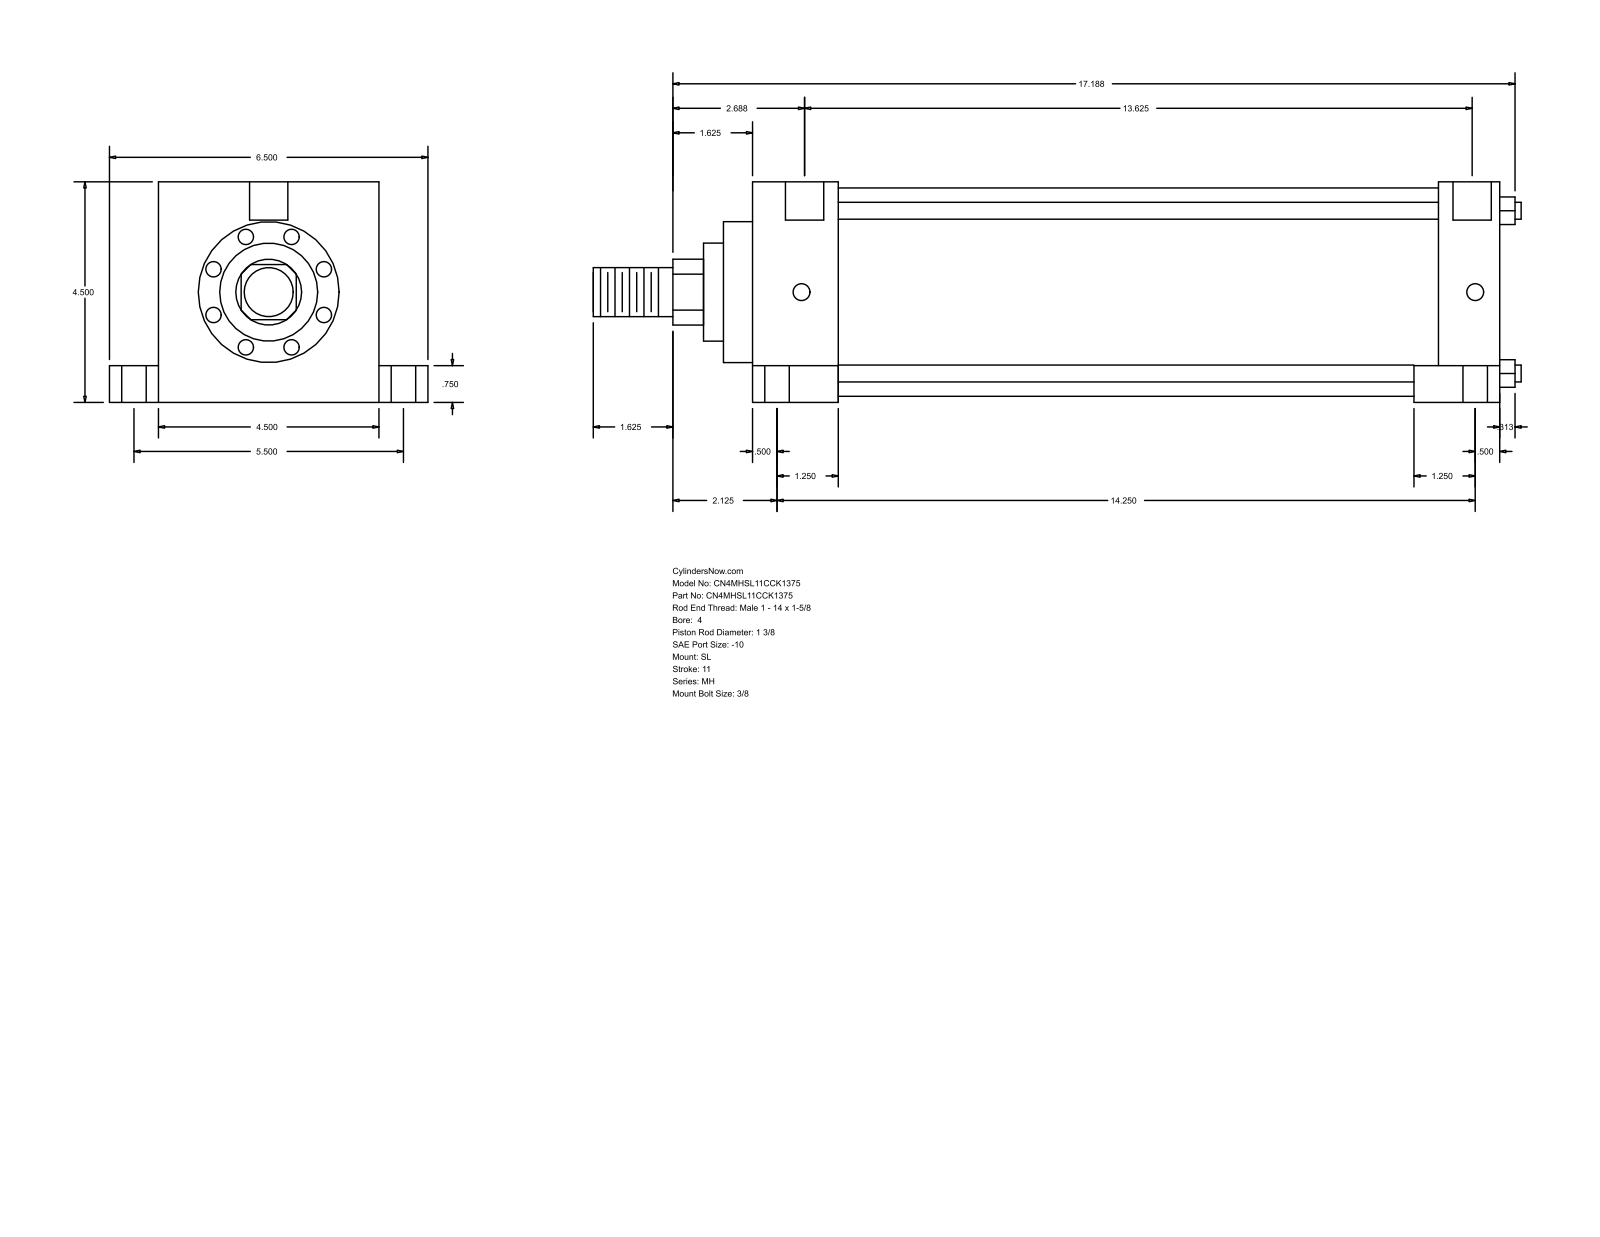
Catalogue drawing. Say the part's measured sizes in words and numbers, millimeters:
The part is named "MH_SL__0400_1.375". Its 3-D file was written by "GSSL Pune (CONFIG_CONTROL_DESIGN)". It is 0 solids with 110 faces: 77 planar, 33 cylindrical and 0 other. Overall it measures 481.01 by 165.1 by 114.3 millimeters. Round holes: 4 of diameter 8.73, 4 of diameter 12.7, 4 of diameter 19.05, 2 of diameter 19.84. Round bosses or shafts: 4 of diameter 8.76, 1 of diameter 107.95, 1 of diameter 73.03, 1 of diameter 50.8, 1 of diameter 34.92, 1 of diameter 25.4. Partial cylindrical surfaces (rounded edges, fillets, slot ends): 1 of radius 17.06. The main face-to-face distances are 114.3, 387.35, 44.45, 342.9, 355.61, 311.16, 31.74, 25.4, 139.7, 19.05. The hole center spacings are 1.59, 69.85, 69.87, 70.99, 71.29, 139.7, 347.67, 349.26.
